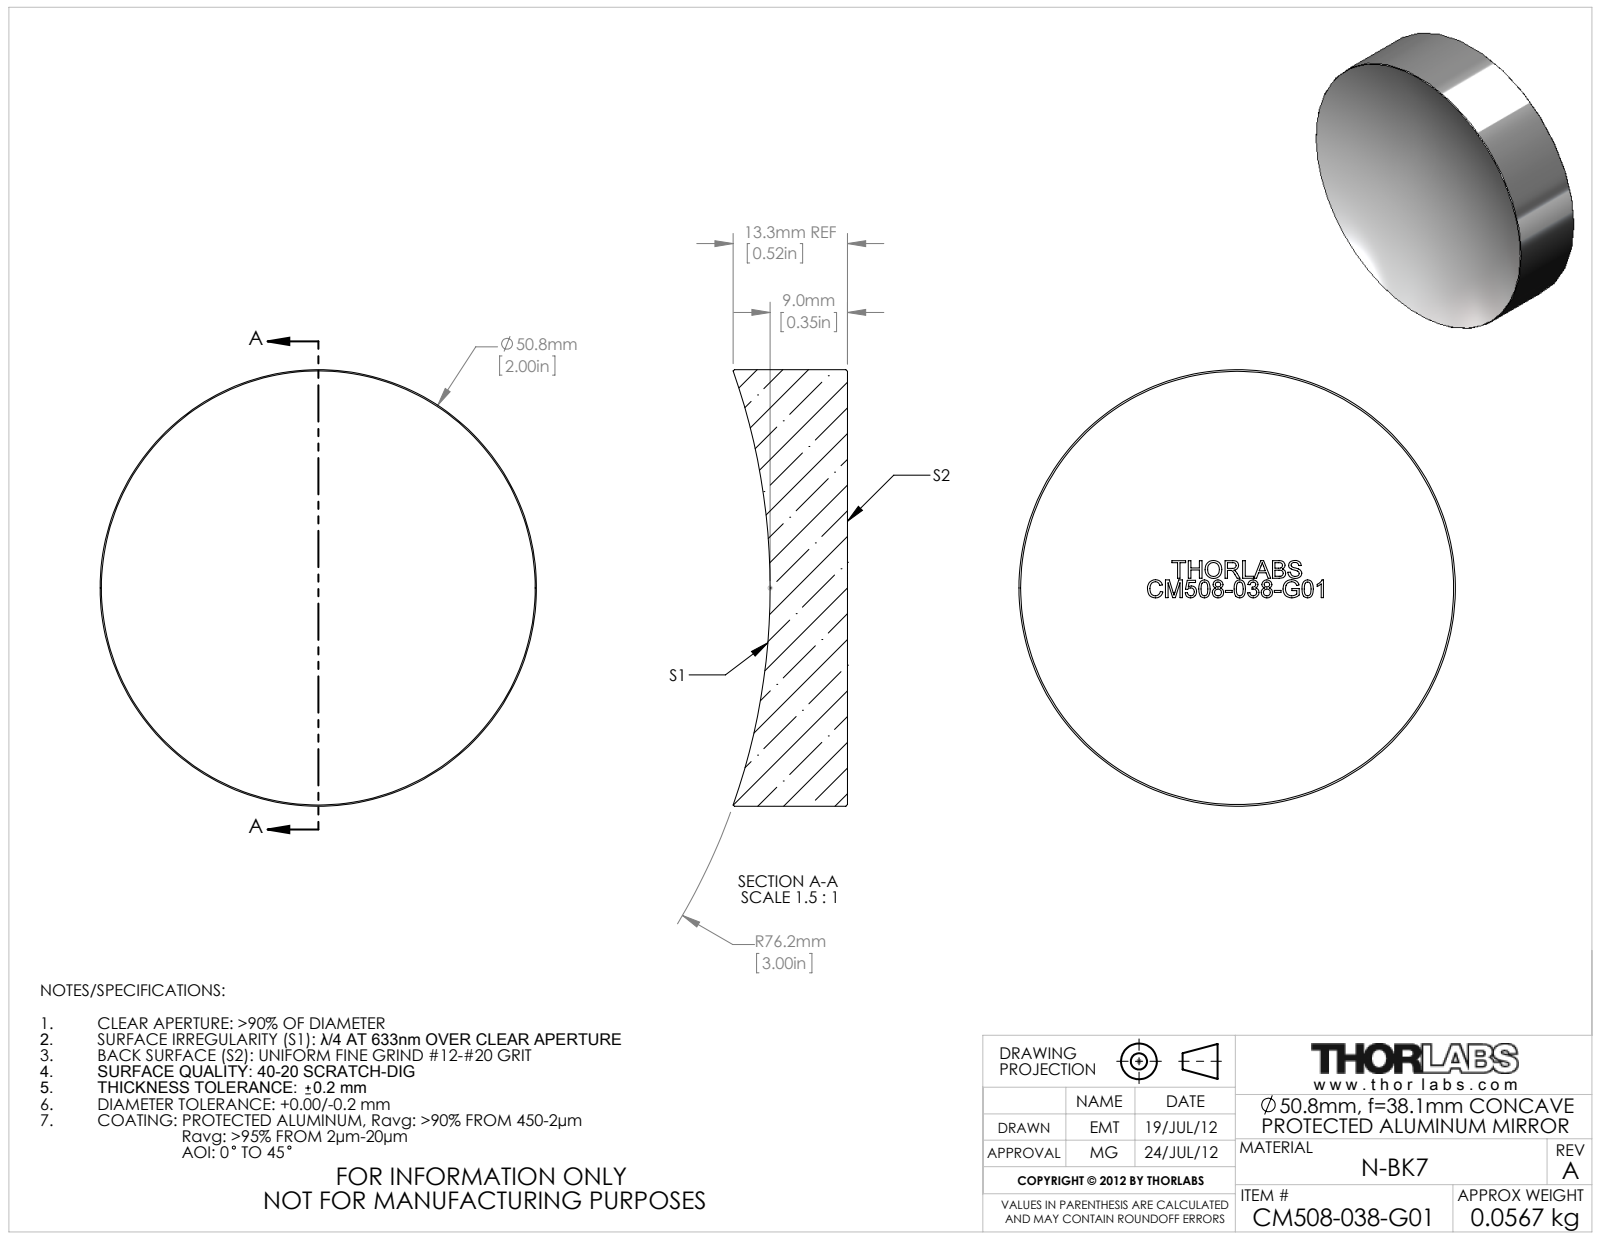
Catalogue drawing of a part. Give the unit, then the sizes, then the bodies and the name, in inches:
Units: inches
Overall size (bounding box): 2 × 2 × 0.524
Round bosses / shafts (diameter × count): ⌀2 ×1
Bodies: 0 solids, 42 faces (34 planar, 2 cylindrical, 6 other)
Part name (STEP PRODUCT): 24634-E0W
STEP written by: SolidWorks 2011 (CONFIG_CONTROL_DESIGN)
